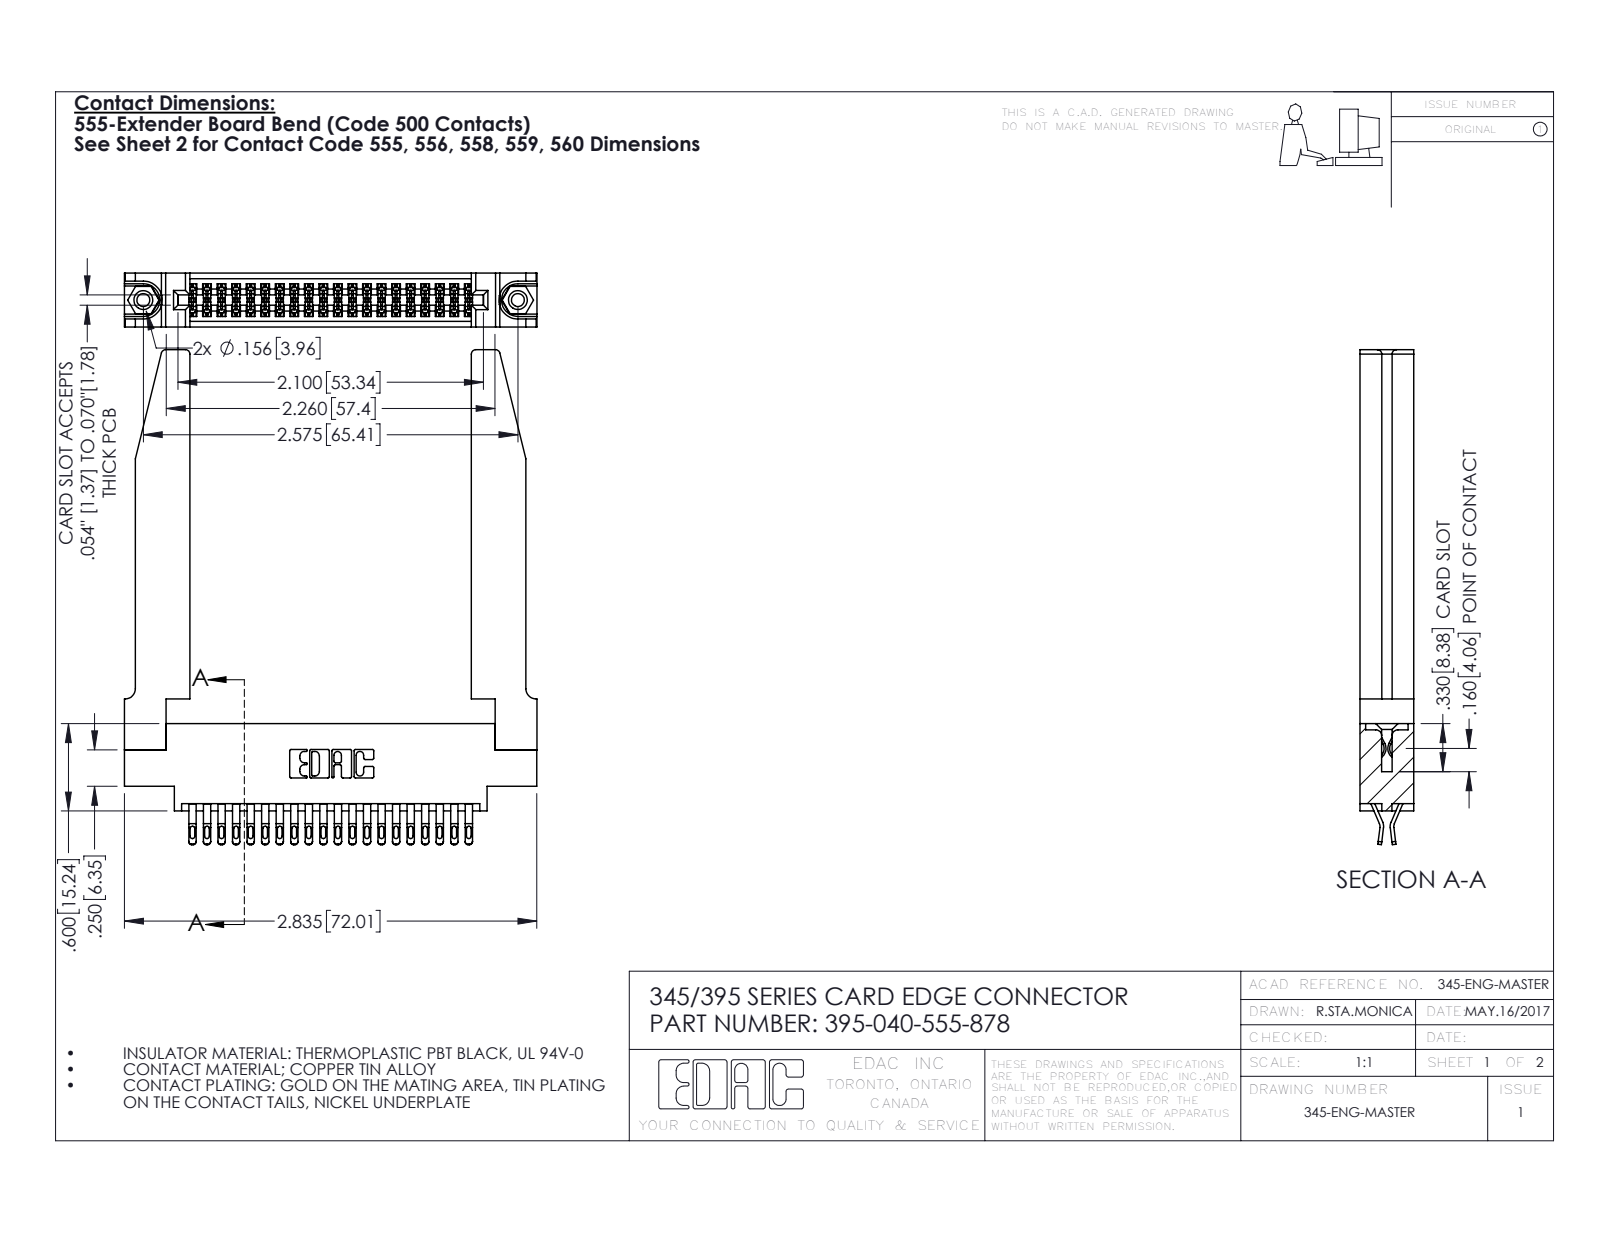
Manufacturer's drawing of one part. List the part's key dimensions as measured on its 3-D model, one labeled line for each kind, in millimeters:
Part name (STEP PRODUCT): 345 Part_0.170 Offset - 0.156 Dia-TH; 345-292-001_555 Tail; 395-040-555-878; 345-250-001_345-250-001-102 (+1 more)
STEP written by: SolidWorks 2016 (CONFIG_CONTROL_DESIGN)
Units: millimetres
Bodies: 45 solids, 2604 faces (1466 planar, 1086 cylindrical, 52 other)
Overall size (bounding box): 86.4 × 72 × 9.4
Volume: 14 600 mm³ · Surface area: 17 010 mm²
Round holes (diameter × count): ⌀2.3 ×2, ⌀3.2 ×2, ⌀4 ×2, ⌀1.6 ×1
Round bosses / shafts (diameter × count): ⌀3.9 ×2
Partial cylindrical surfaces — rounded edges, fillets, slot ends (radius × count): R0.4 ×100, R0.5 ×80, R0.2 ×60, R0.3 ×22, R0.8 ×8, R0.2 ×6, R0.8 ×6, R0.7 ×3
Main face-to-face distances: 9.4, 1.8, 7.6, 0.6, 2.5, 6.9, 5.1, 3.8, 3.8, 5.7
Hole centre spacings: 6.9, 59.5, 65.4
